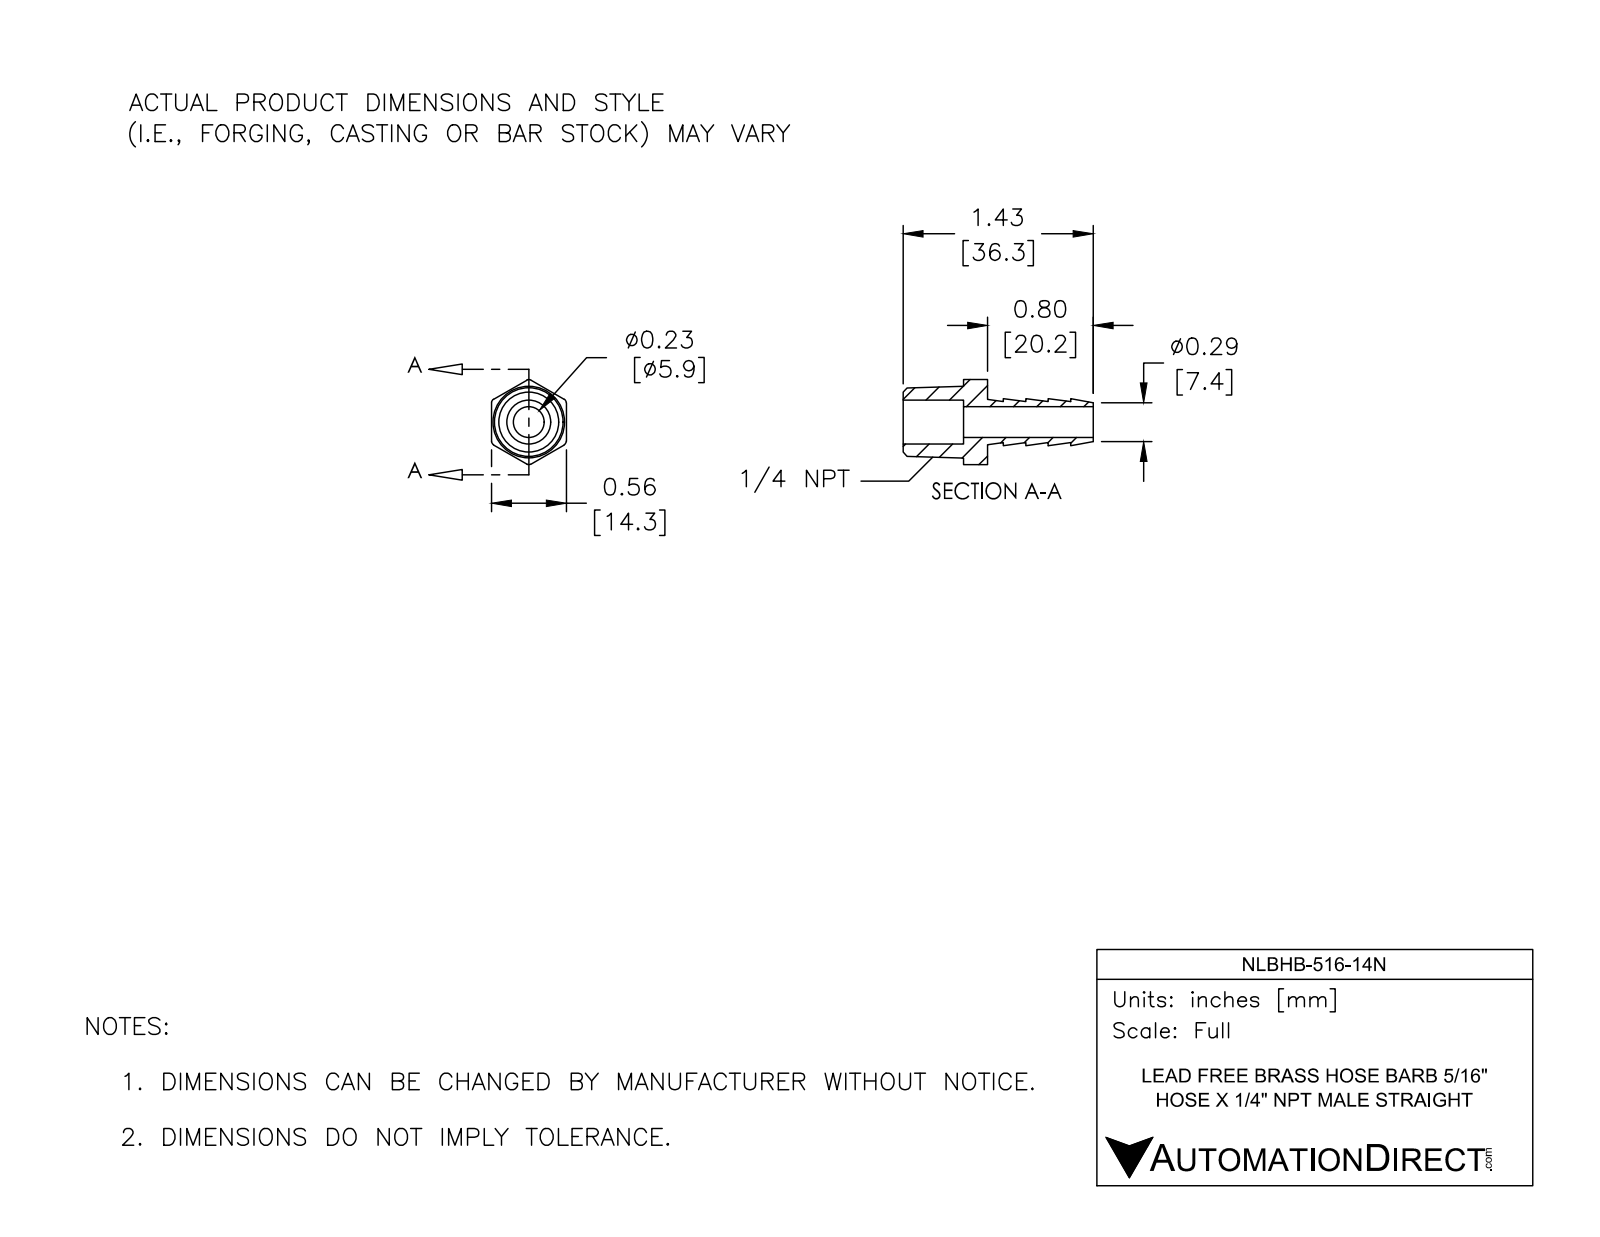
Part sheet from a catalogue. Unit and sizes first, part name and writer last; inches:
Units: inches
Overall size (bounding box): 1.43 × 0.64 × 0.562
Round holes (diameter × count): ⌀0.232 ×1, ⌀0.33 ×1
Partial cylindrical surfaces — rounded edges, fillets, slot ends (radius × count): R0.03 ×6
Main face-to-face distances: 0.562, 0.18, 0.635, 0.455, 0.169, 0.338, 0.507, 0.795, 0.975, 1.43
Volume: 0.136 in³ · Surface area: 3.604 in²
Bodies: 1 solid, 39 faces (15 planar, 10 cylindrical, 14 other)
Part name (STEP PRODUCT): NLBHB-516-14N
STEP written by: SolidWorks 2017 (AUTOMOTIVE_DESIGN)
